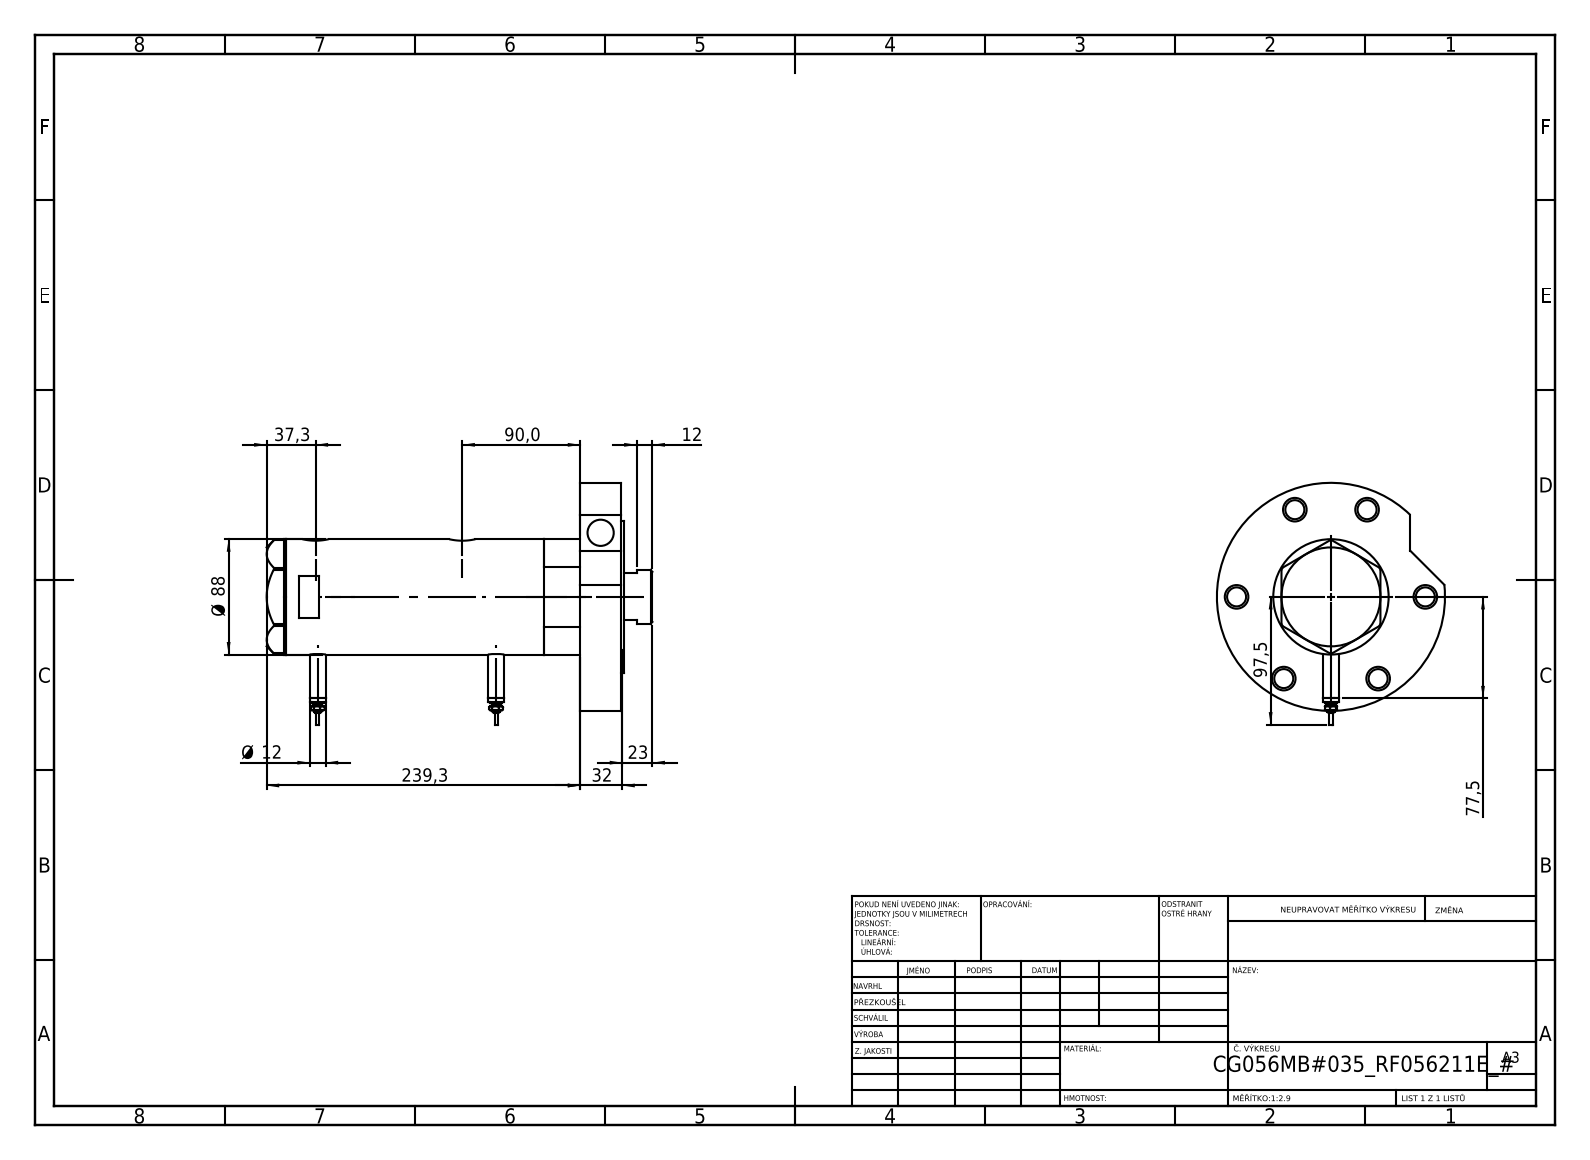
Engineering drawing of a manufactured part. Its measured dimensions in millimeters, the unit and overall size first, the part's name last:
Units: millimetres
Overall size (bounding box): 294.3 × 184.5 × 174
Round holes (diameter × count): ⌀14.5 ×7, ⌀18 ×6, ⌀20 ×3, ⌀12.5 ×2, ⌀13.16 ×2, ⌀42 ×1, ⌀43.5 ×1, ⌀56 ×1, ⌀60 ×1, ⌀75 ×1, ⌀80 ×1
Round bosses / shafts (diameter × count): ⌀12 ×2, ⌀9 ×2, ⌀7 ×2, ⌀4.5 ×2, ⌀2.5 ×2, ⌀174 ×1, ⌀116 ×1, ⌀88 ×1
Main face-to-face distances: 31, 2, 257.3, 224.3, 255.3, 33, 134.4, 89.9, 120.9, 122.9
Hole centre spacings: 72, 80, 119.73, 124.71, 129.15, 143.69, 1.7, 25.8
Volume: 2 077 000 mm³ · Surface area: 302 918 mm²
Bodies: 7 solids, 257 faces (91 planar, 102 cylindrical, 64 other)
Part name (STEP PRODUCT): V270CG_MIDDLE; Switch; V270CG_RF211E; V270CG_FRONT (+2 more)
STEP written by: SolidWorks 2019 (CONFIG_CONTROL_DESIGN)
